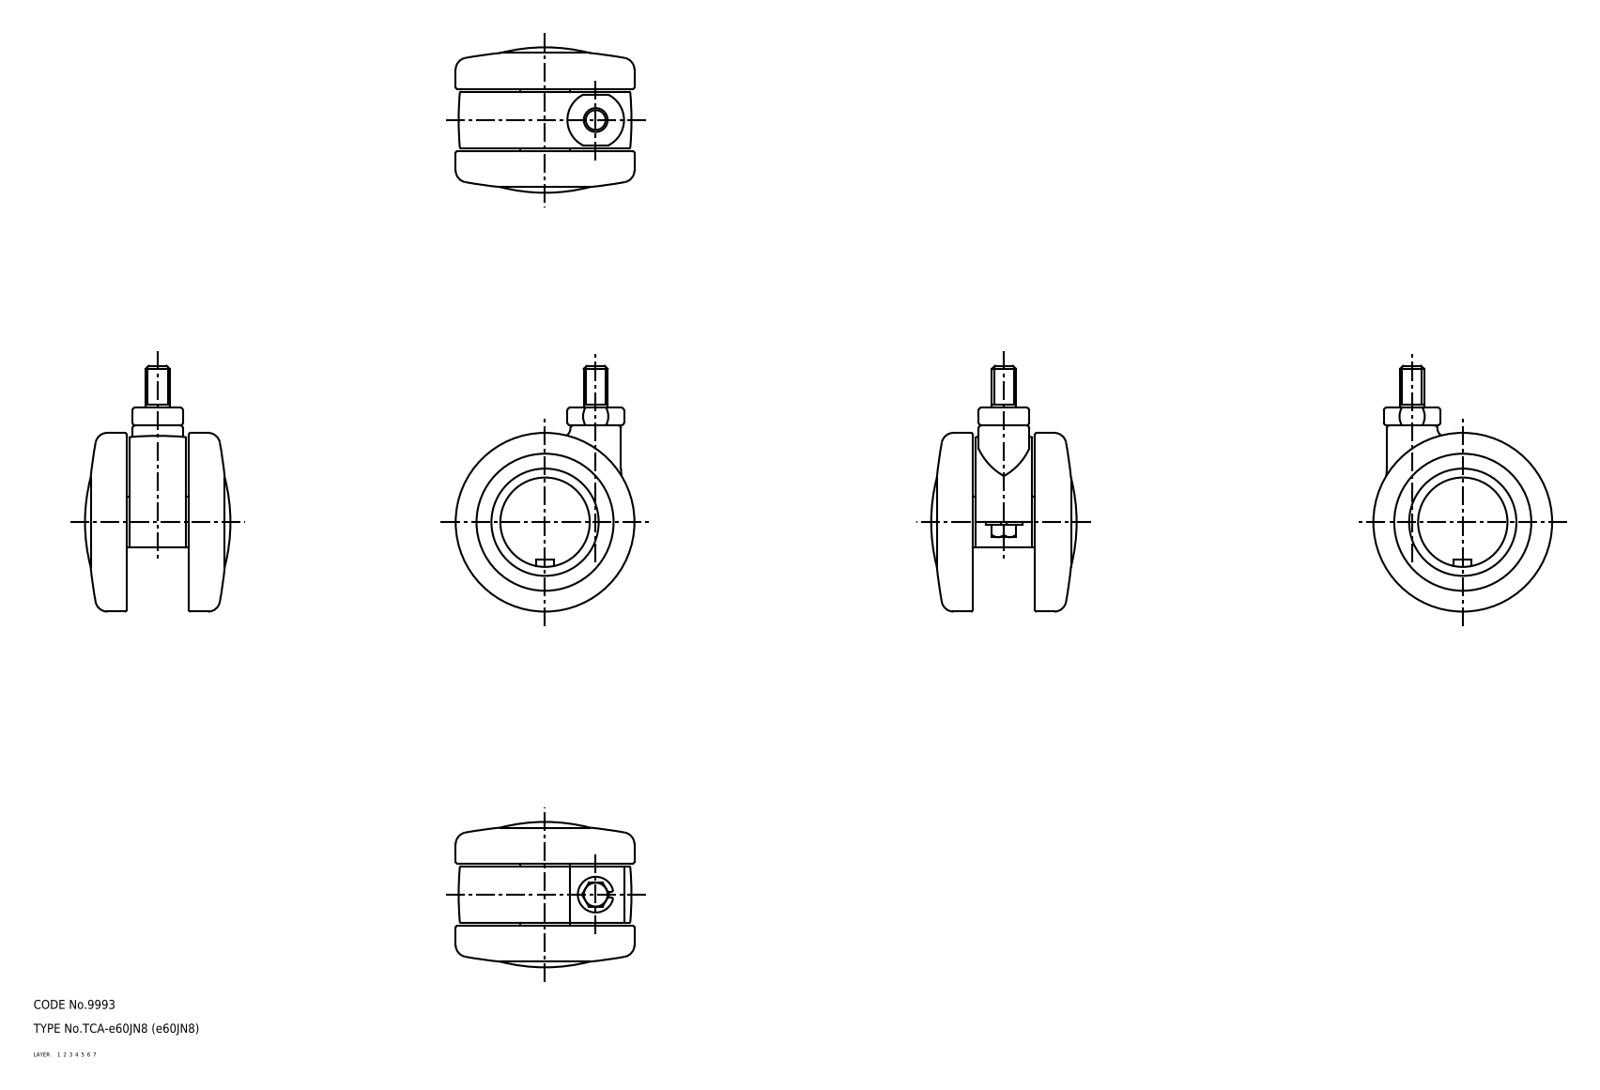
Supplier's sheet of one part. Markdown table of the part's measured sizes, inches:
| quantity | value |
| --- | --- |
| part name | wheel_mr; wheel; main shaft; e60JN8_4136_36 |
| STEP written by | CADfix (AUTOMOTIVE_DESIGN) |
| units | inches |
| bodies | 4 solids, 140 faces (0 planar, 0 cylindrical, 140 other) |
| overall size | 3.248 × 2.362 × 1.922 |
| volume | 5.198 in³ |
| surface area | 47.46 in² |
